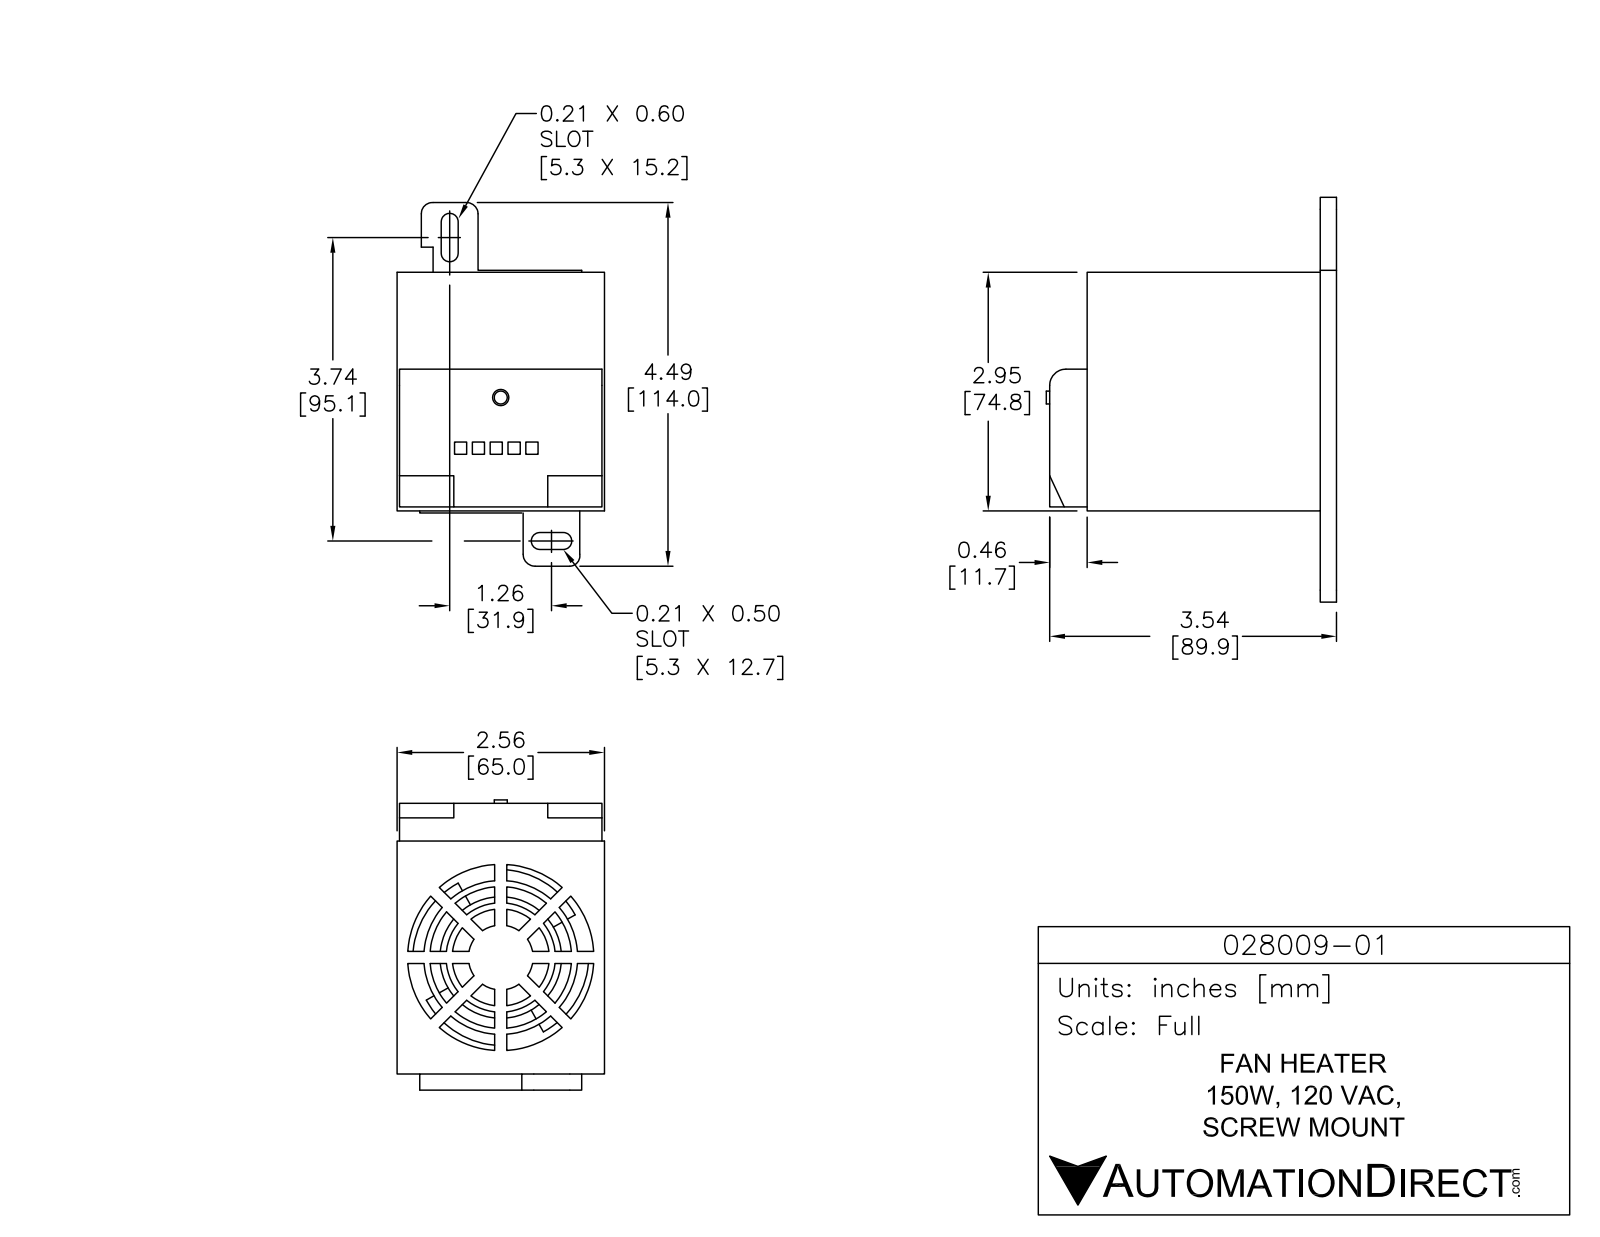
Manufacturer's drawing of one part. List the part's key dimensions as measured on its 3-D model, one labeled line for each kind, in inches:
Part name (STEP PRODUCT): 028009-01
STEP written by: SolidWorks 2013 (AUTOMOTIVE_DESIGN)
Units: inches
Bodies: 1 solid, 359 faces (182 planar, 138 cylindrical, 39 other)
Overall size (bounding box): 4.51 × 3.43 × 2.545
Volume: 23.42 in³ · Surface area: 61.47 in²
Round holes (diameter × count): ⌀0.275 ×1, ⌀2.27 ×1
Round bosses / shafts (diameter × count): ⌀0.22 ×1
Partial cylindrical surfaces — rounded edges, fillets, slot ends (radius × count): R0.065 ×44, R0.02 ×30, R0.08 ×4, R0.1 ×4, R0.105 ×4, R0.17 ×1, R0.232 ×1, R0.25 ×1
Main face-to-face distances: 2.545, 2.865, 0.1, 0.16, 3.43, 3.27, 0.035, 2.51, 2.965, 2.765
